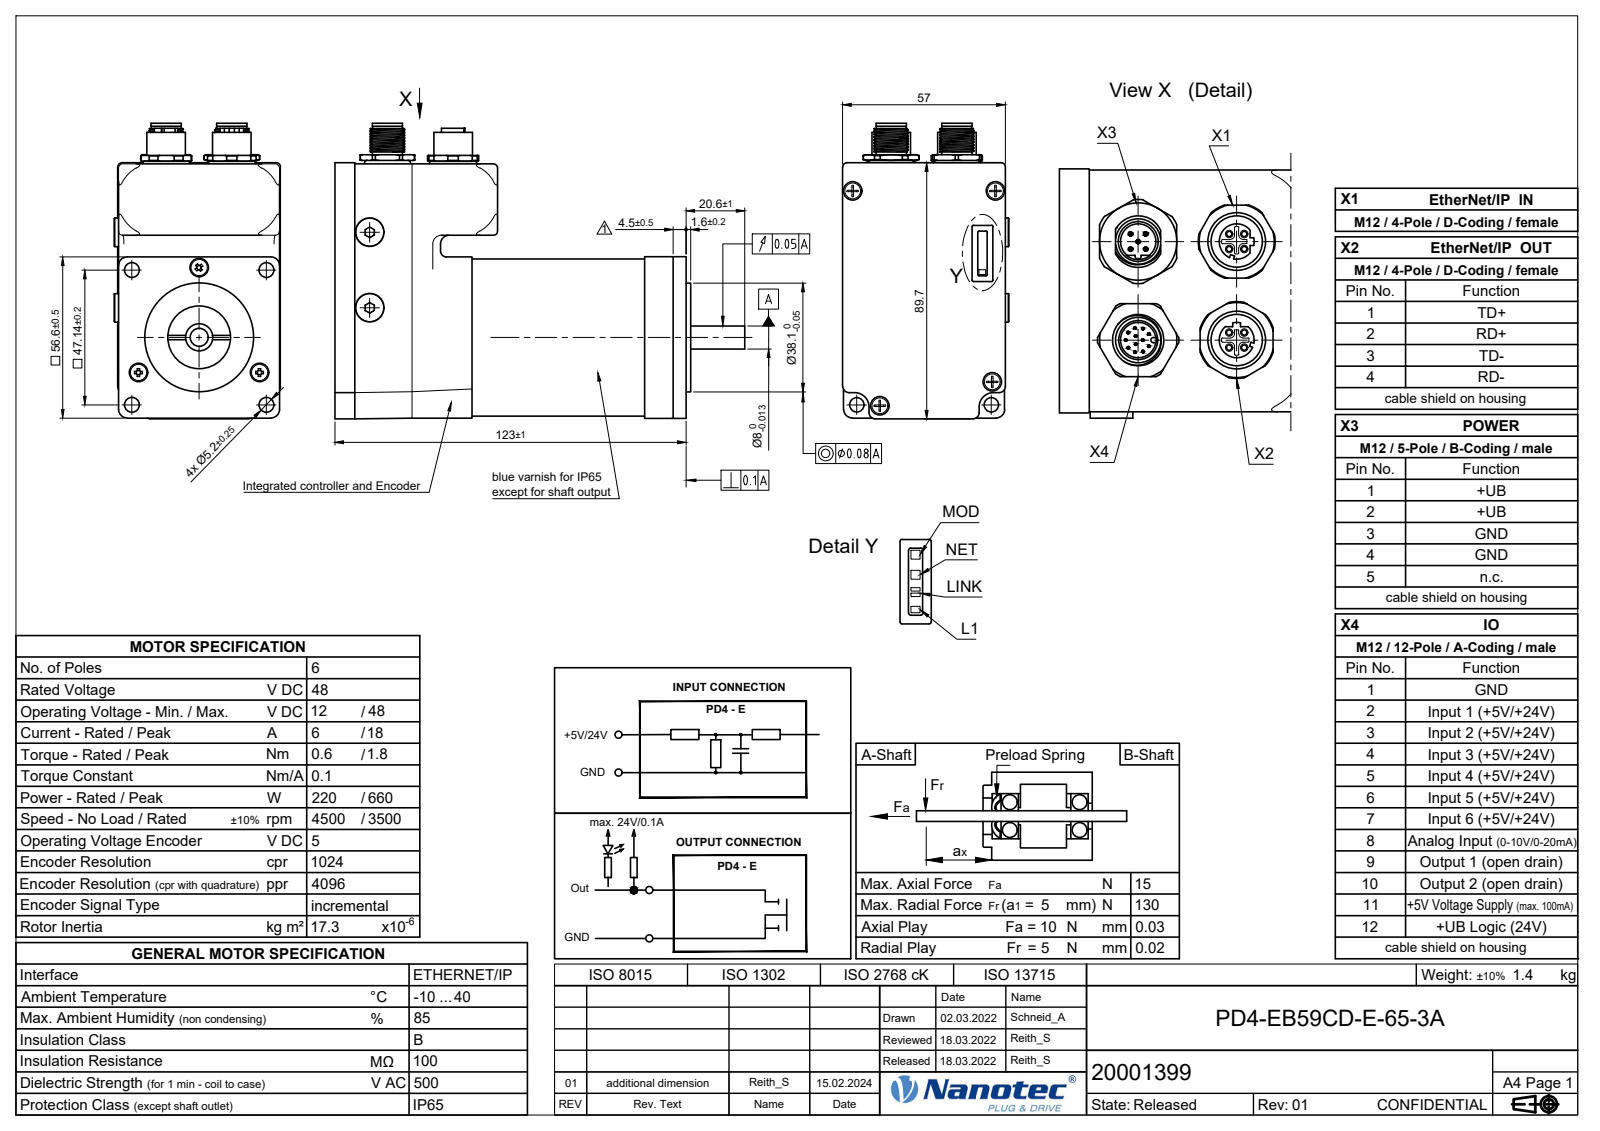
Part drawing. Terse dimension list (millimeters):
name: D-00005317
written by: Autodesk Inventor 2021 (AUTOMOTIVE_DESIGN)
unit: mm
bodies: 15 solids, 1145 faces (438 planar, 359 cylindrical, 348 other)
size: 143.6 × 103.5 × 58.5
volume: 324 596 mm³; area: 77 675 mm²
holes: 8× ⌀1.2, 6× ⌀2.46, 4× ⌀3.4, 4× ⌀5.2, 4× ⌀15.3, 3× ⌀6.5, 3× ⌀11, 2× ⌀6, 2× ⌀12, 1× ⌀8.3, 1× ⌀10, 1× ⌀15.4
bosses: 17× ⌀1, 13× ⌀1.6, 12× ⌀0.6, 4× ⌀5.5, 4× ⌀3, 4× ⌀2.69, 3× ⌀15.2, 2× ⌀14
rounds: 24× R2, 16× R0.3, 16× R0.5, 12× R0.2, 12× R1.5, 8× R1, 7× R3, 4× R2.2
face distances: 8, 48, 40, 2.5, 27, 19, 21, 53.9, 123, 115
hole spacings: 2.5, 3.54, 21.3, 23, 24.83, 5.01, 23.27, 32.62
